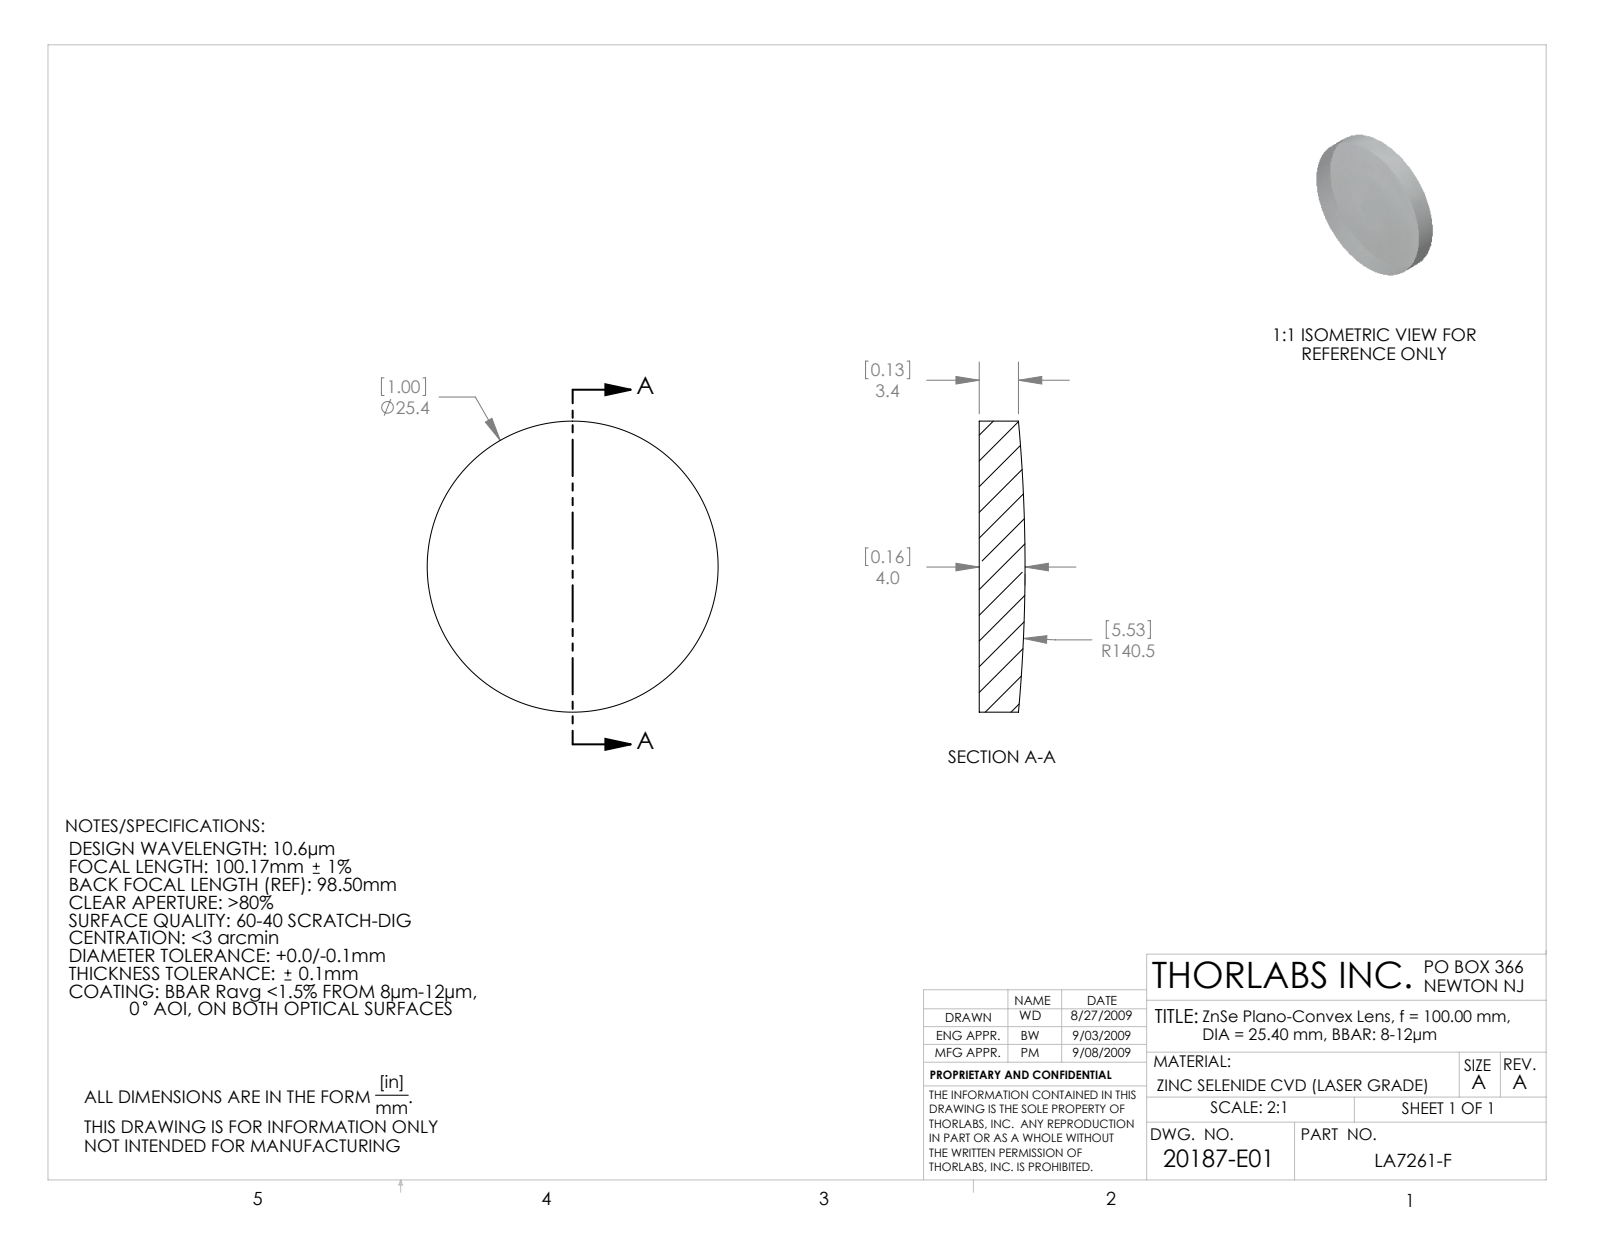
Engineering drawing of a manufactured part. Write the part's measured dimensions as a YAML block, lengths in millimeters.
part_name: "20187-E0W"
step_written_by: "SolidWorks 2007 (CONFIG_CONTROL_DESIGN)"
units: millimeters
bodies: {solids: 1, faces: 5, planar: 1, cylindrical: 2, other: 2}
overall_size: [25.4, 25.4, 4]
volume: 1881
surface_area: 1288
round_bosses_or_shafts:
  - {diameter: 25.4, count: 1}
